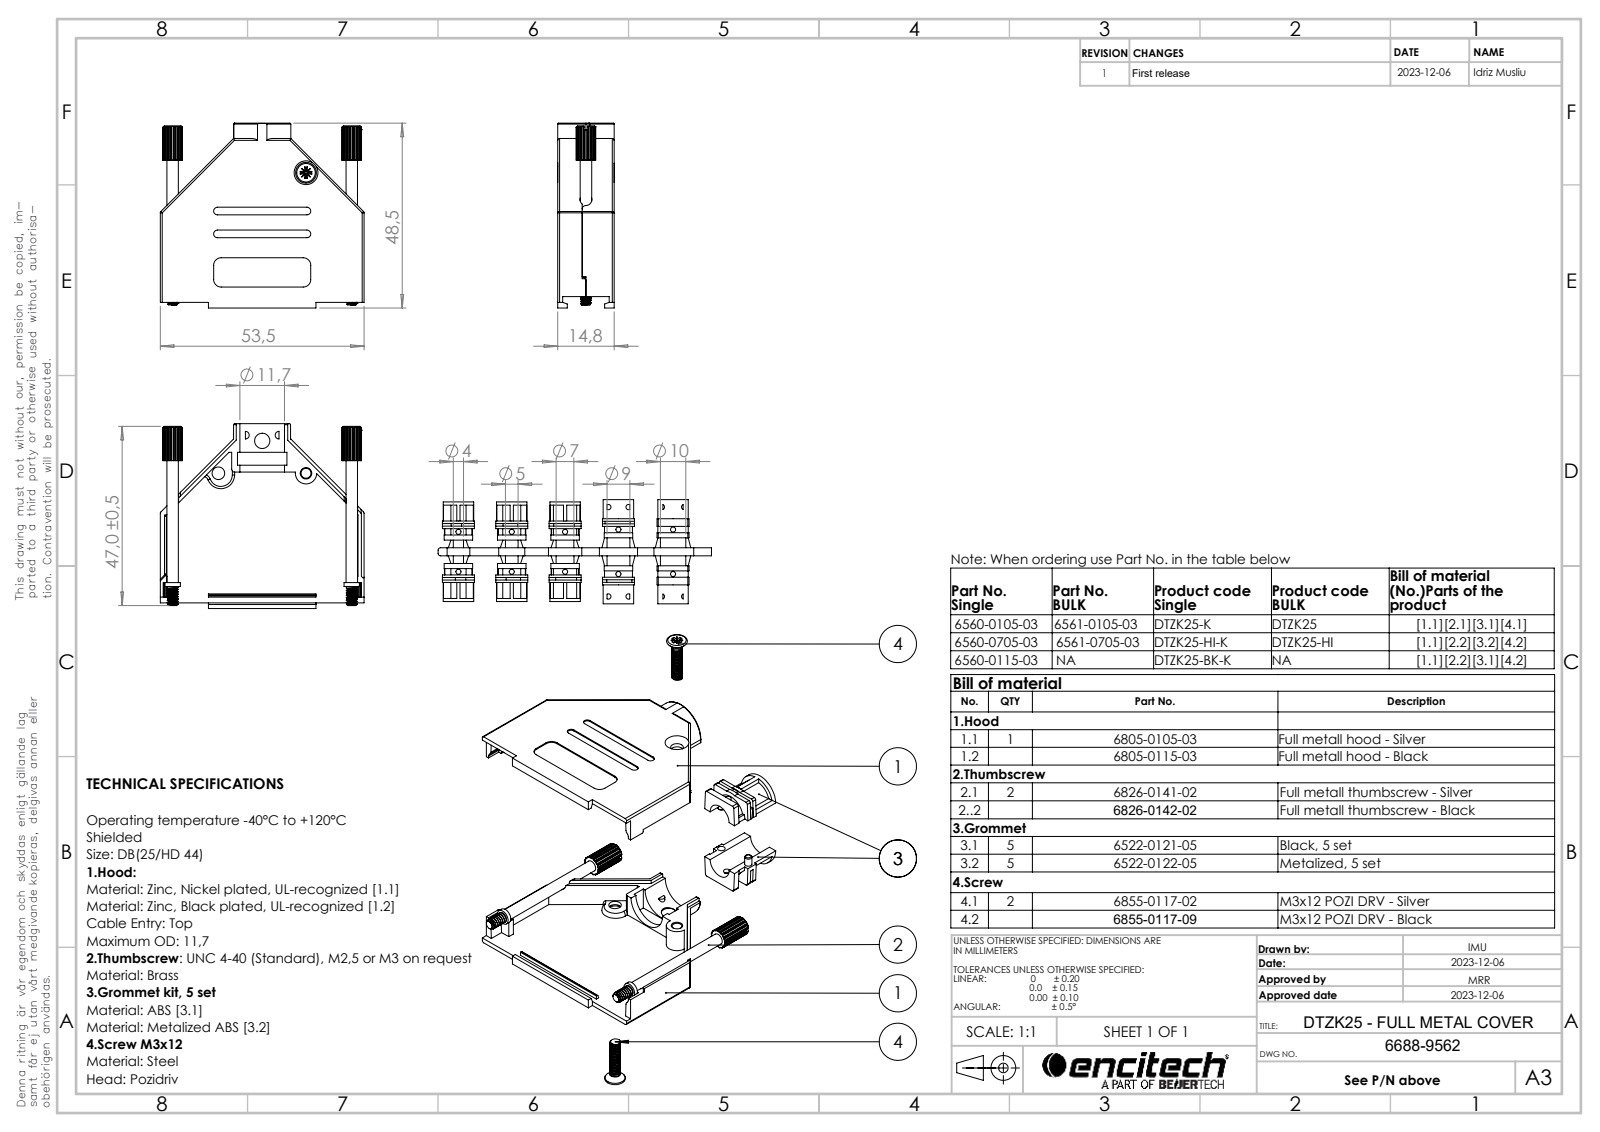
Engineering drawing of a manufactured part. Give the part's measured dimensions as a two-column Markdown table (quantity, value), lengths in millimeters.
| quantity | value |
| --- | --- |
| part name | 6688-9562; 6522-0121-05 (7mm); 6826-0141-02; 6855-0117-02 (+1 more) |
| STEP written by | SolidWorks 2021 (AUTOMOTIVE_DESIGN) |
| units | millimeters |
| bodies | 8 solids, 816 faces (434 planar, 304 cylindrical, 78 other) |
| overall size | 53.5 × 48.5 × 14.85 |
| volume | 9 970 mm³ |
| surface area | 15 366 mm² |
| round holes (diameter × count) | 2 × 3, 2.6 × 2, 3.1 × 2, 3.3 × 2, 4 × 1, 7 × 1, 11.7 × 1 |
| round bosses / shafts (diameter × count) | 4 × 2, 3 × 2, 2.9 × 2, 2.85 × 2, 1.9 × 2, 15 × 1, 11.6 × 1, 9.2 × 1 |
| partial cylindrical surfaces (radius × count) | 0.5 × 24, 1 × 12, 0.1 × 8, 0.25 × 8, 0.2 × 6, 2 × 4, 5.91 × 4, 0.3 × 2 |
| main face-to-face distances | 1.3, 13.5, 14.8, 12.2, 6.1, 1.6, 7.4, 1, 7.1, 14.5 |
| hole center spacings | 5.71, 6.97, 7.45, 11.54, 14.3, 16.9, 23.5, 7.6 |
